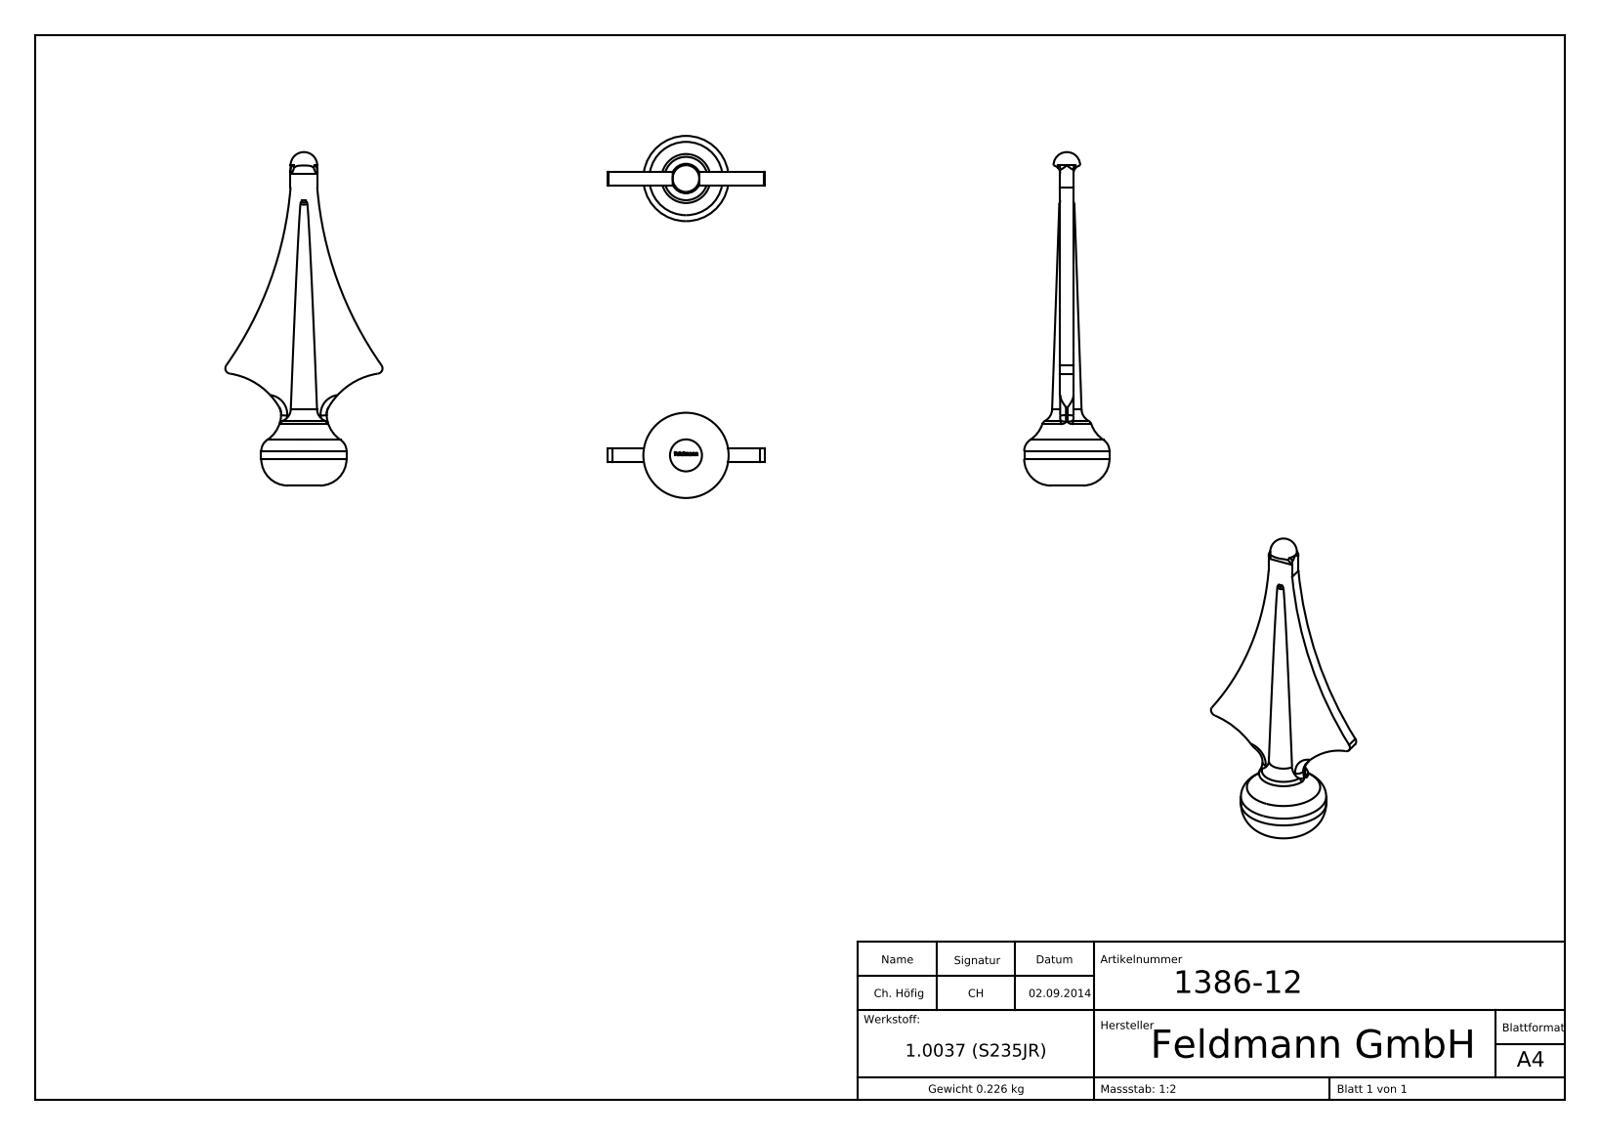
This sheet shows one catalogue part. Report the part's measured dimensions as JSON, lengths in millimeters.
{"part_name": "1386-12", "step_written_by": "SolidWorks 2015 (CONFIG_CONTROL_DESIGN)", "units": "millimeters", "bodies": {"solids": 1, "faces": 180, "planar": 70, "cylindrical": 13, "other": 97}, "overall_size": [125.2, 59, 32], "volume_mm3": 29010, "surface_area_mm2": 9399, "round_bosses_or_shafts": [[32, 1]], "partial_cylinders_radius": [[2, 4], [3, 2], [26, 2], [134.68, 2]], "face_to_face_distances": [5, 10, 0.5, 2.5, 0.39, 2.97, 1.53, 1.12, 2.85, 4.09]}
